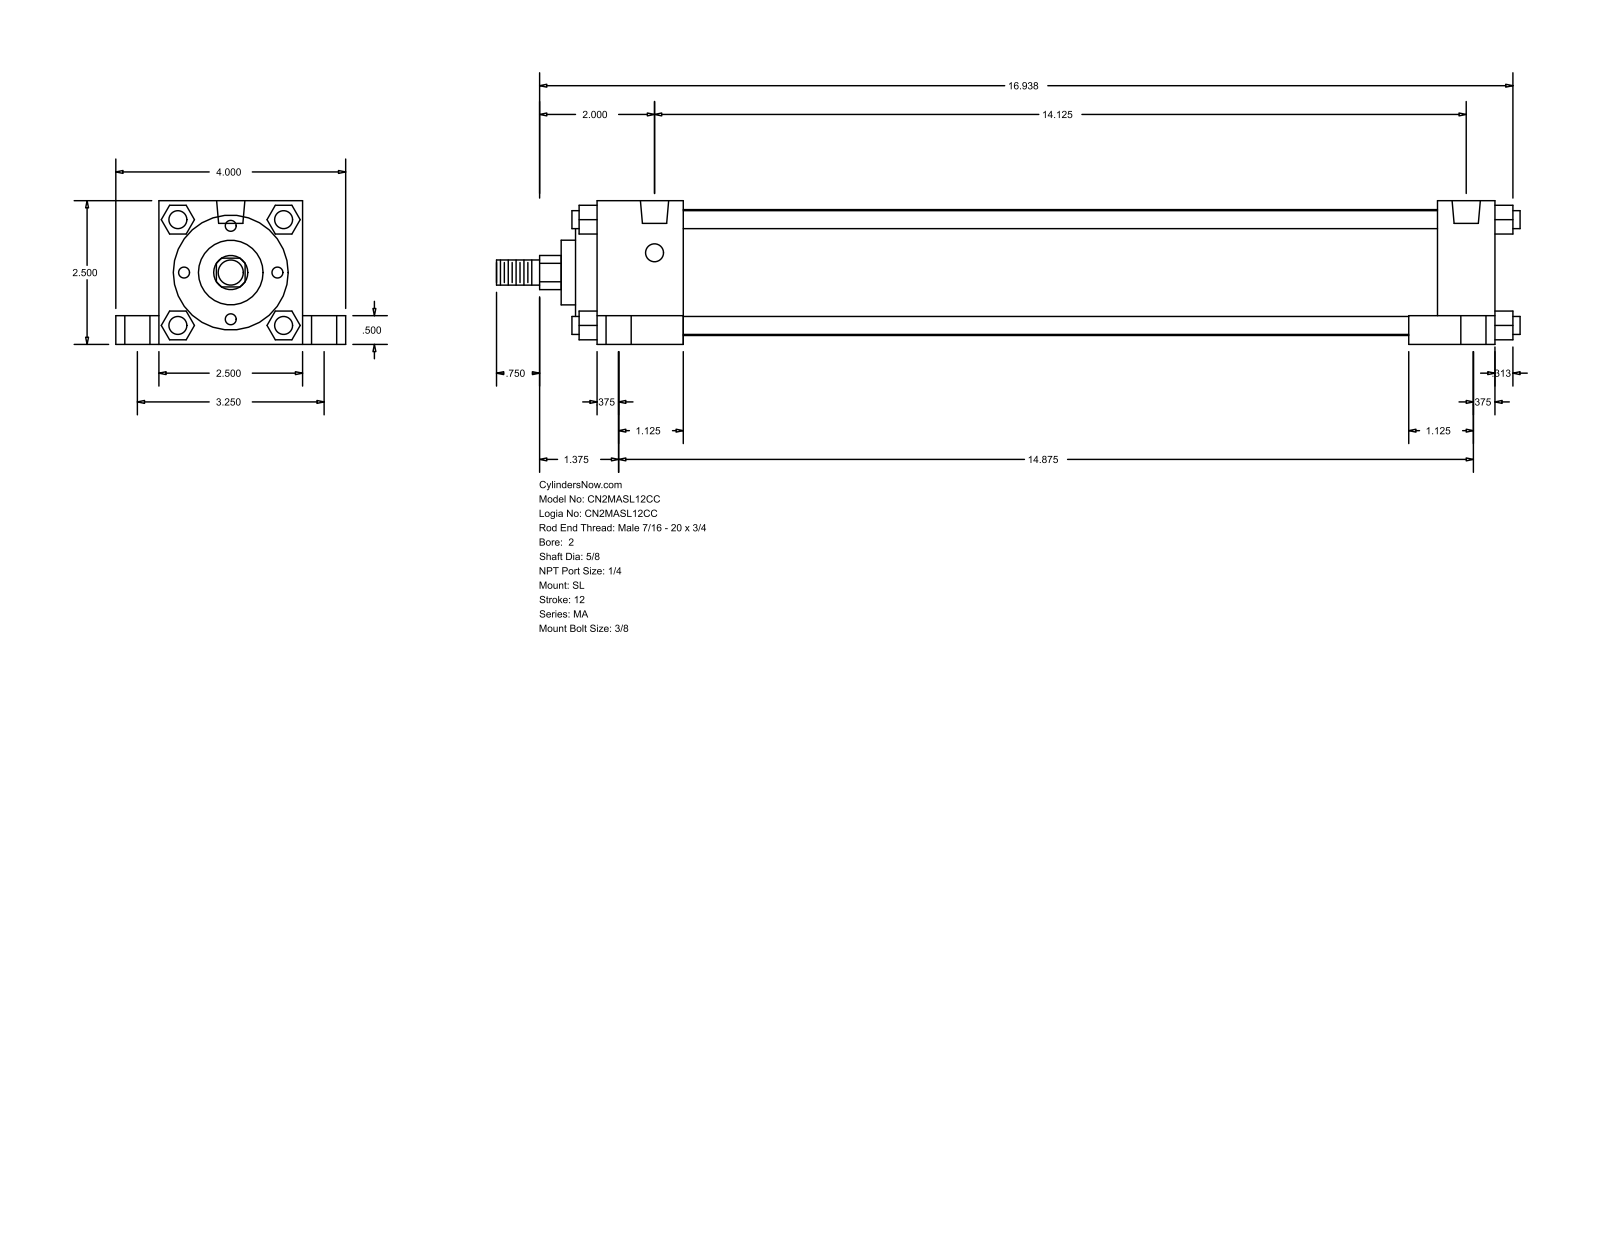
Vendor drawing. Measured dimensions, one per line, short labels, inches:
name: MA_SL__0200_0.625
written by: GSSL Pune (CONFIG_CONTROL_DESIGN)
unit: in
bodies: 0 solids, 150 faces (113 planar, 37 cylindrical, 0 other)
size: 17.813 × 4 × 2.5
holes: 4× ⌀0.313, 4× ⌀0.437, 4× ⌀0.687, 2× ⌀0.492
bosses: 4× ⌀0.313, 1× ⌀2.19, 1× ⌀2, 1× ⌀1.125, 1× ⌀0.625, 1× ⌀0.437
rounds: 1× R0.297
face distances: 2.5, 0.5, 0.375, 0.75, 3.25, 1.5, 2, 15.625, 14.125, 14.625
hole spacings: 1.63, 1.741, 3.25, 14.125, 14.343, 14.839, 14.875, 15.226
